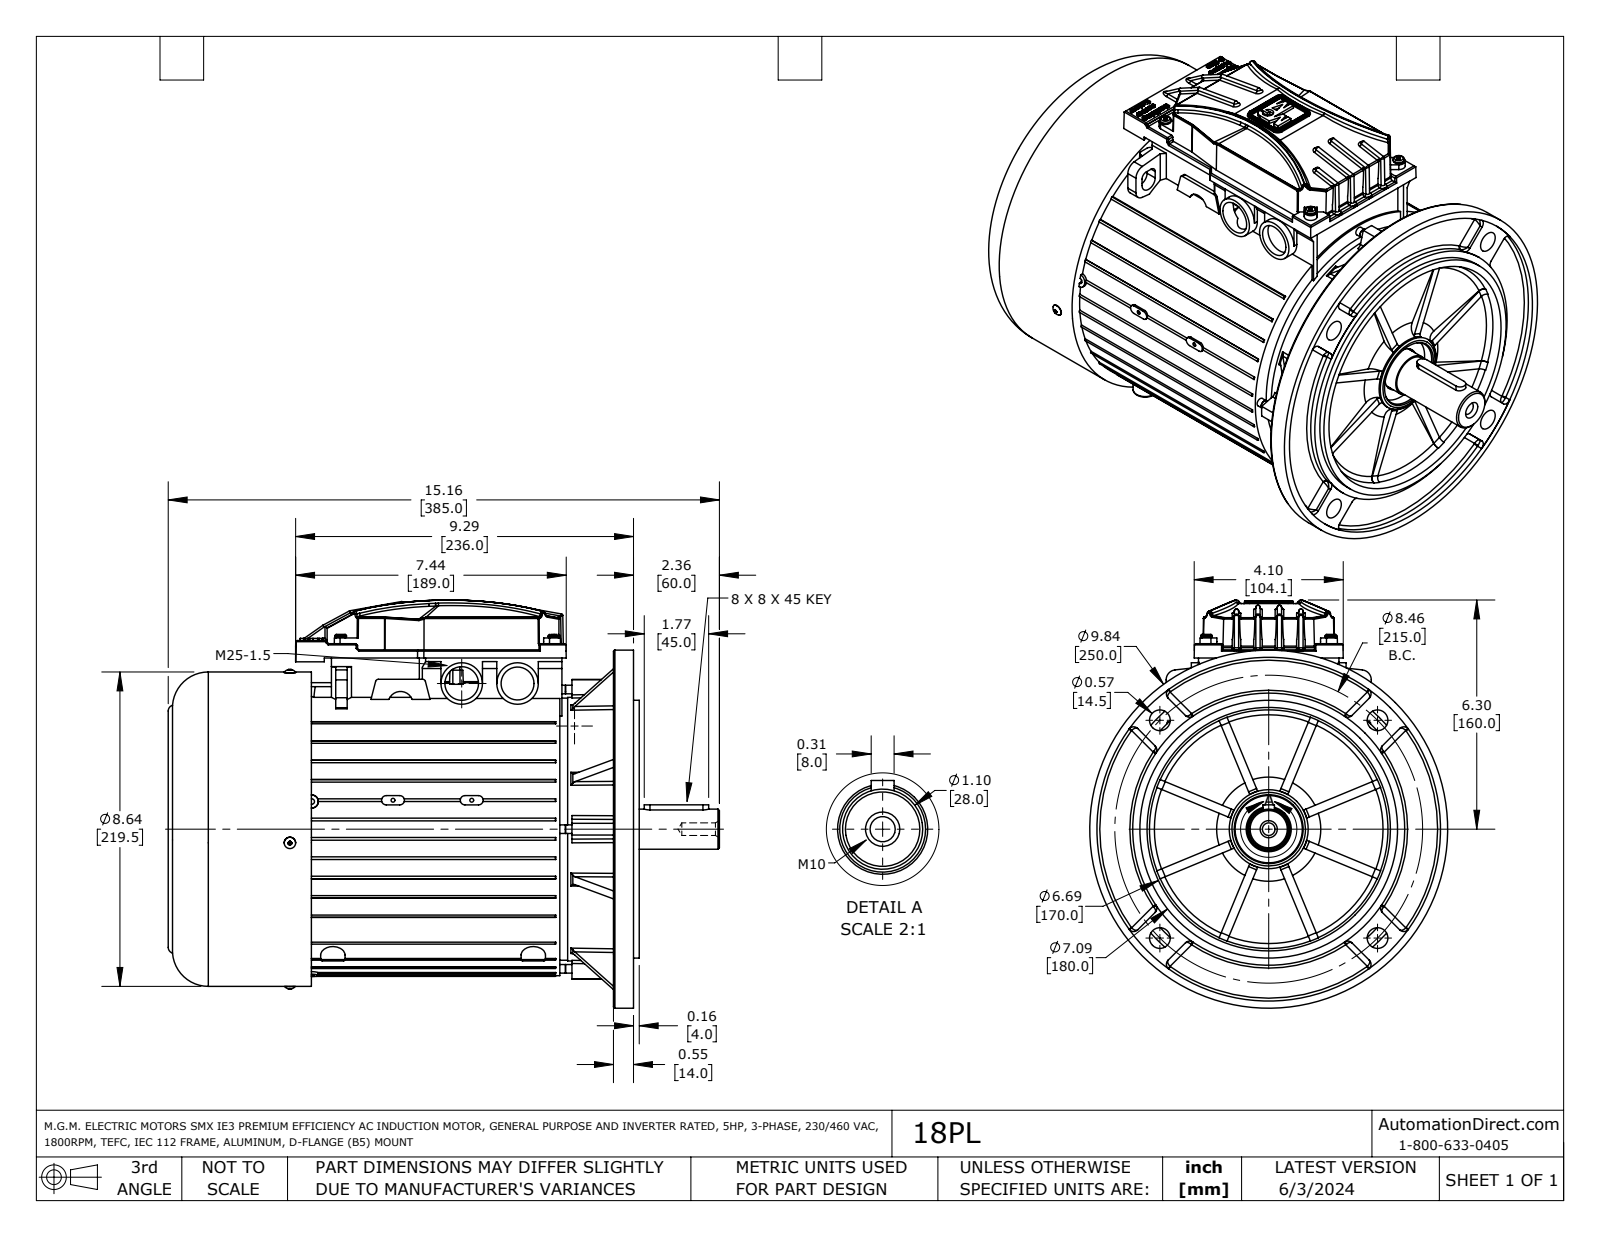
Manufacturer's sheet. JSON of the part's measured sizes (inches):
{"part_name": "18PL", "step_written_by": "SolidWorks 2021 (AUTOMOTIVE_DESIGN)", "units": "inches", "bodies": {"solids": 18, "faces": 3282, "planar": 1613, "cylindrical": 636, "other": 1033}, "overall_size": [15.157, 11.221, 9.843], "volume_in3": 606.3, "surface_area_in2": 1021, "round_holes": [[0.098, 5], [0.13, 5], [0.15, 4], [0.177, 4], [0.197, 4], [0.315, 4], [0.571, 4], [0.106, 2], [0.118, 2], [0.165, 2], [0.346, 1], [0.906, 1]], "round_bosses_or_shafts": [[0.315, 8], [0.138, 6], [0.236, 4], [0.079, 4], [1.142, 2], [9.843, 1], [8.642, 1], [8.054, 1]], "partial_cylinders_radius": [[0.016, 48], [0.059, 47], [0.039, 38], [0.157, 38], [0.008, 32], [0.004, 24], [0.02, 16], [0.033, 16]], "face_to_face_distances": [0.236, 0.177, 10.631, 1.613, 12.244, 1.791, 12.421, 0.02, 12.441, 12.264], "hole_center_spacings": [3.11, 7.458, 3.839, 4.232, 5.429, 5.985, 0.611, 0.672]}
